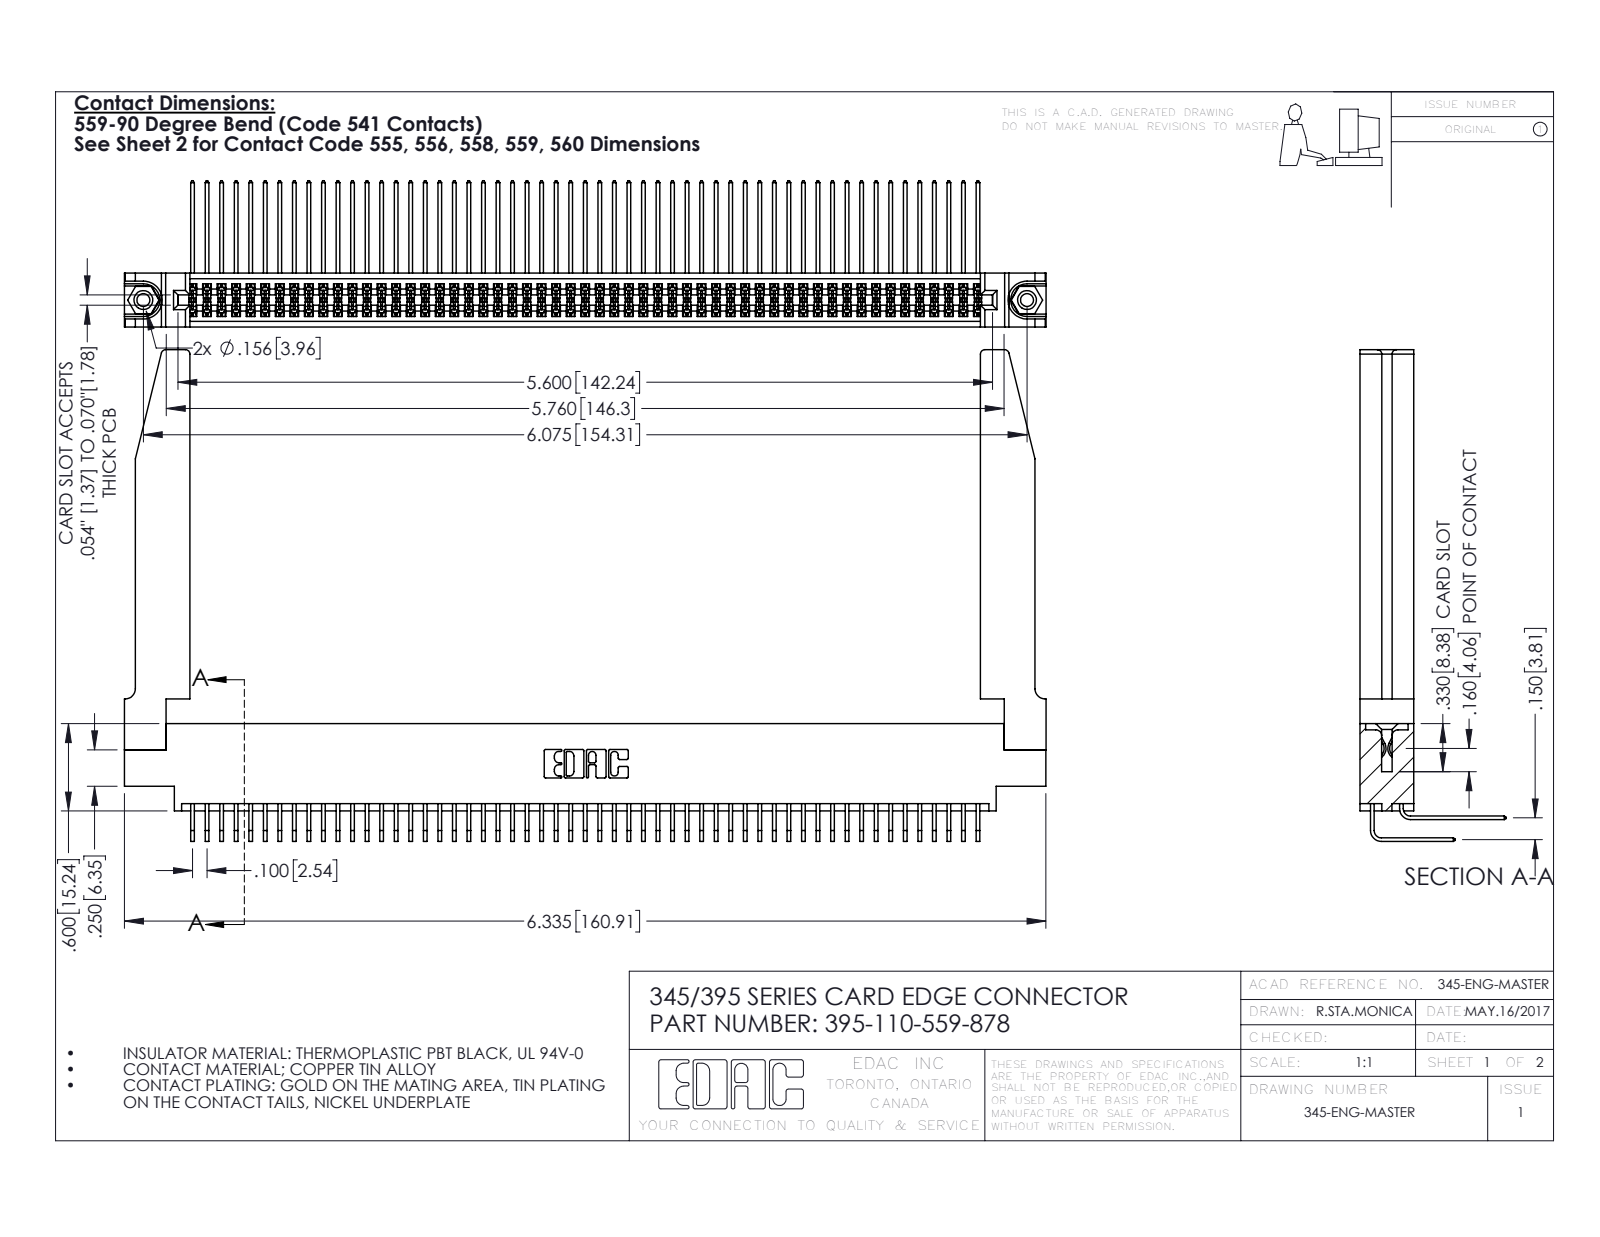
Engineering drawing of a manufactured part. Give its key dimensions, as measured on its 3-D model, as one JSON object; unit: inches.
{"part_name": "345-220-078_345-220-078; 345-292-001_559 Tail - 2; 345 Part_0.170 Offset - 0.156 Dia-TH; 345-250-001_345-250-001-102 (+2 more)", "step_written_by": "SolidWorks 2016 (CONFIG_CONTROL_DESIGN)", "units": "inches", "bodies": {"solids": 115, "faces": 6084, "planar": 4076, "cylindrical": 1956, "other": 52}, "overall_size": [6.336, 3.379, 1.005], "volume_in3": 1.467, "surface_area_in2": 53.13, "round_holes": [[0.089, 2], [0.125, 2], [0.156, 2], [0.064, 1]], "round_bosses_or_shafts": [[0.155, 2]], "partial_cylinders_radius": [[0.006, 165], [0.01, 22], [0.03, 8], [0.007, 6], [0.031, 6], [0.026, 3], [0.014, 2], [0.019, 2]], "face_to_face_distances": [0.072, 0.37, 0.298, 0.098, 0.272, 0.025, 0.2, 0.225, 0.15, 0.175], "hole_center_spacings": [0.27, 5.839, 6.075]}
